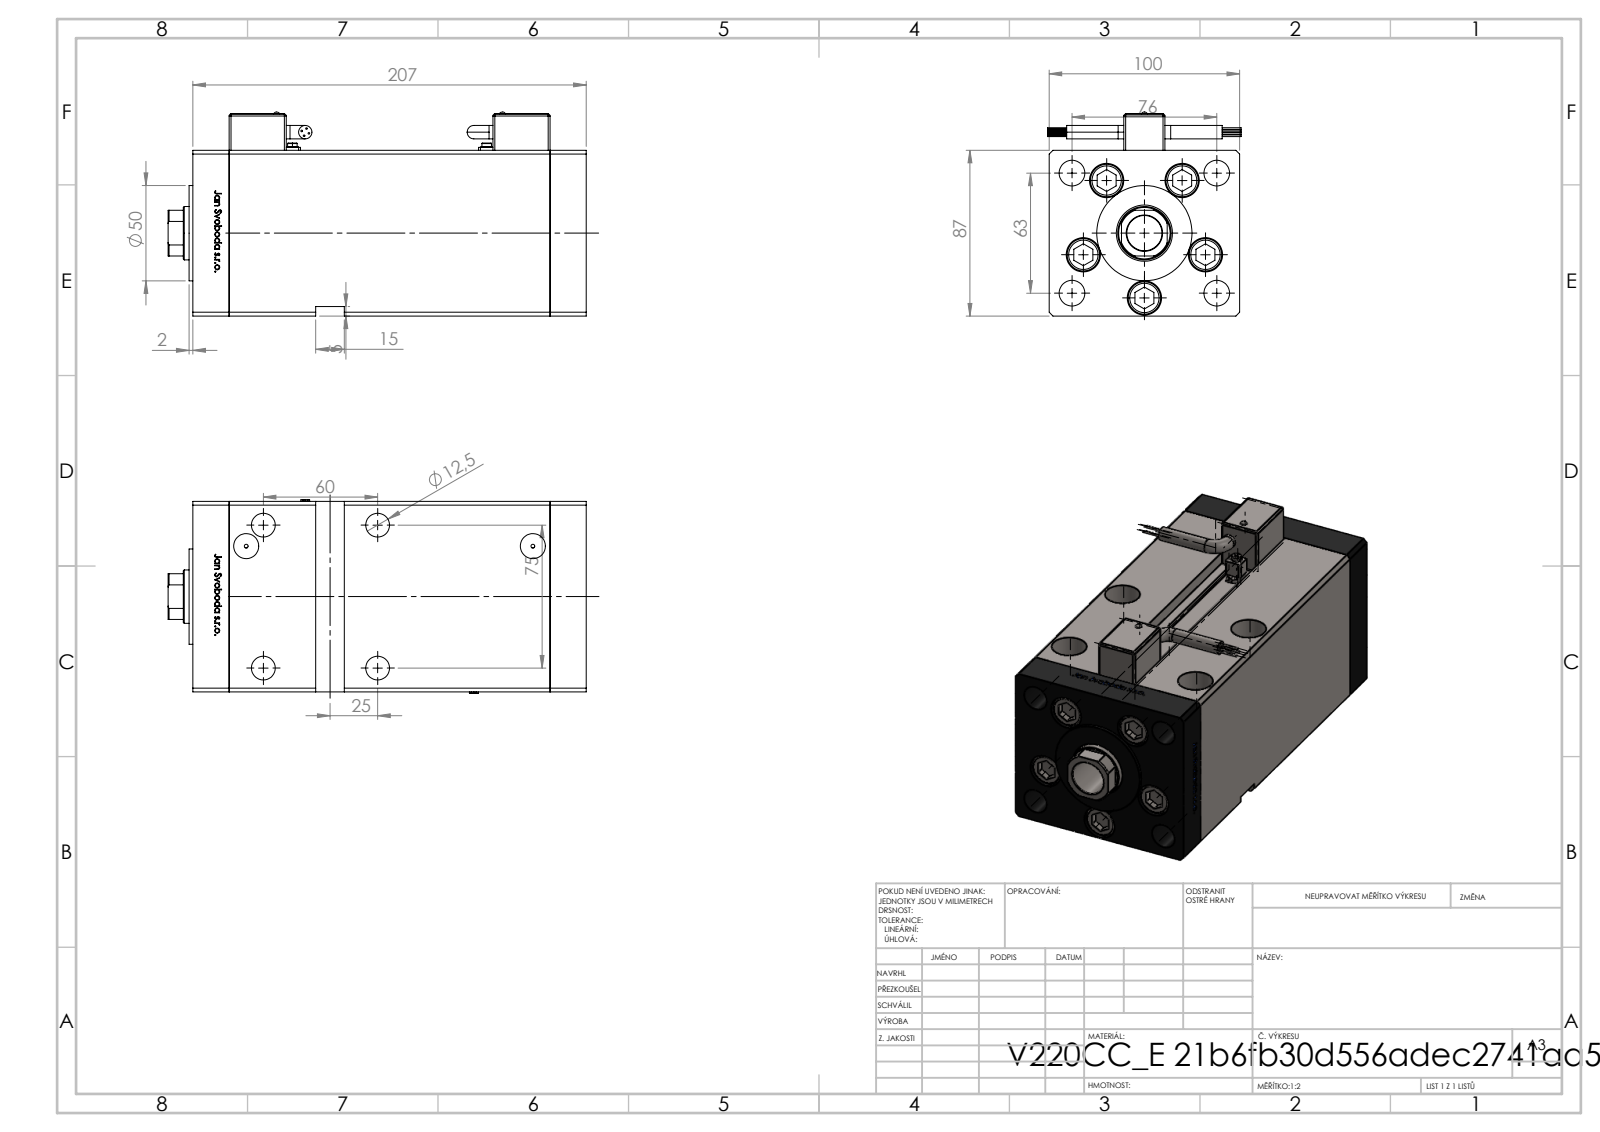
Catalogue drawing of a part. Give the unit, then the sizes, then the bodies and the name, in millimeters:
Units: millimetres
Overall size (bounding box): 219.5 × 107.1 × 101.6
Round holes (diameter × count): ⌀13.5 ×11, ⌀18 ×5, ⌀18.5 ×5, ⌀12.5 ×4, ⌀2 ×2, ⌀3.6 ×2, ⌀5 ×2, ⌀7 ×2, ⌀13.16 ×2, ⌀28 ×1, ⌀29.5 ×1
Round bosses / shafts (diameter × count): ⌀0.85 ×8, ⌀17 ×5, ⌀8 ×5, ⌀7 ×4, ⌀6 ×2, ⌀3.5 ×2, ⌀2.5 ×2, ⌀50 ×1
Partial cylindrical surfaces — rounded edges, fillets, slot ends (radius × count): R1 ×24, R4 ×4, R0.93 ×2, R13.5 ×1
Main face-to-face distances: 100, 87, 19, 168.5, 187.5, 34.25, 206.5, 15.25, 153.25, 172.25
Hole centre spacings: 34, 18.59, 39.64, 49.36, 57.95, 8.25, 21.03, 30.96
Volume: 1 546 000 mm³ · Surface area: 244 893 mm²
Bodies: 16 solids, 1418 faces (553 planar, 255 cylindrical, 610 other)
Part name (STEP PRODUCT): ALLEN BOLT; V220C_VC_E; V220C_E MIDDLE; Magnetic_Switch_MSU4 (+2 more)
STEP written by: SolidWorks 2019 (CONFIG_CONTROL_DESIGN)
